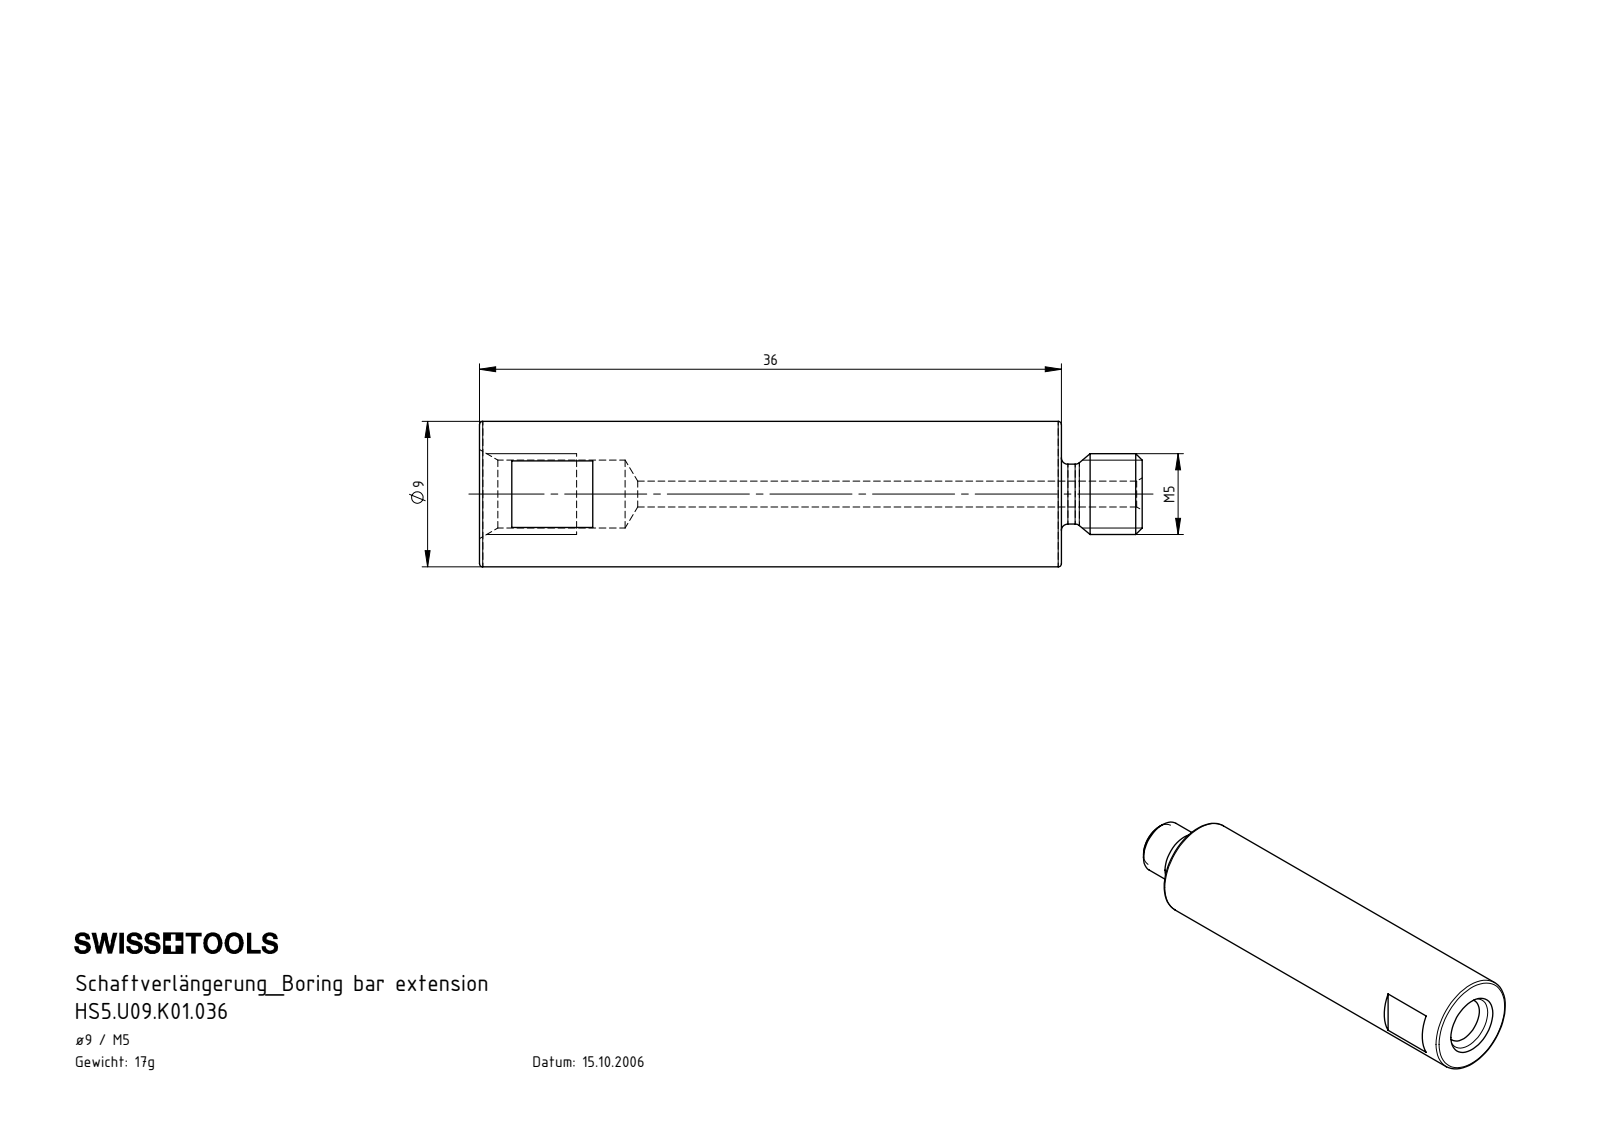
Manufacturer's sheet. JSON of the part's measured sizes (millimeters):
{"part_name": "5-U.9.K01.036_A", "step_written_by": "SolidWorks 2017 (AUTOMOTIVE_DESIGN)", "units": "millimeters", "bodies": {"solids": 1, "faces": 37, "planar": 9, "cylindrical": 10, "other": 18}, "overall_size": [41, 9, 9], "volume_mm3": 2162, "surface_area_mm2": 1491, "round_holes": [[1.6, 1], [4.2, 1]], "round_bosses_or_shafts": [[9, 1], [5, 1], [3.7, 1]], "face_to_face_distances": [36, 8, 5, 41, 34, 29, 7, 39, 2]}
